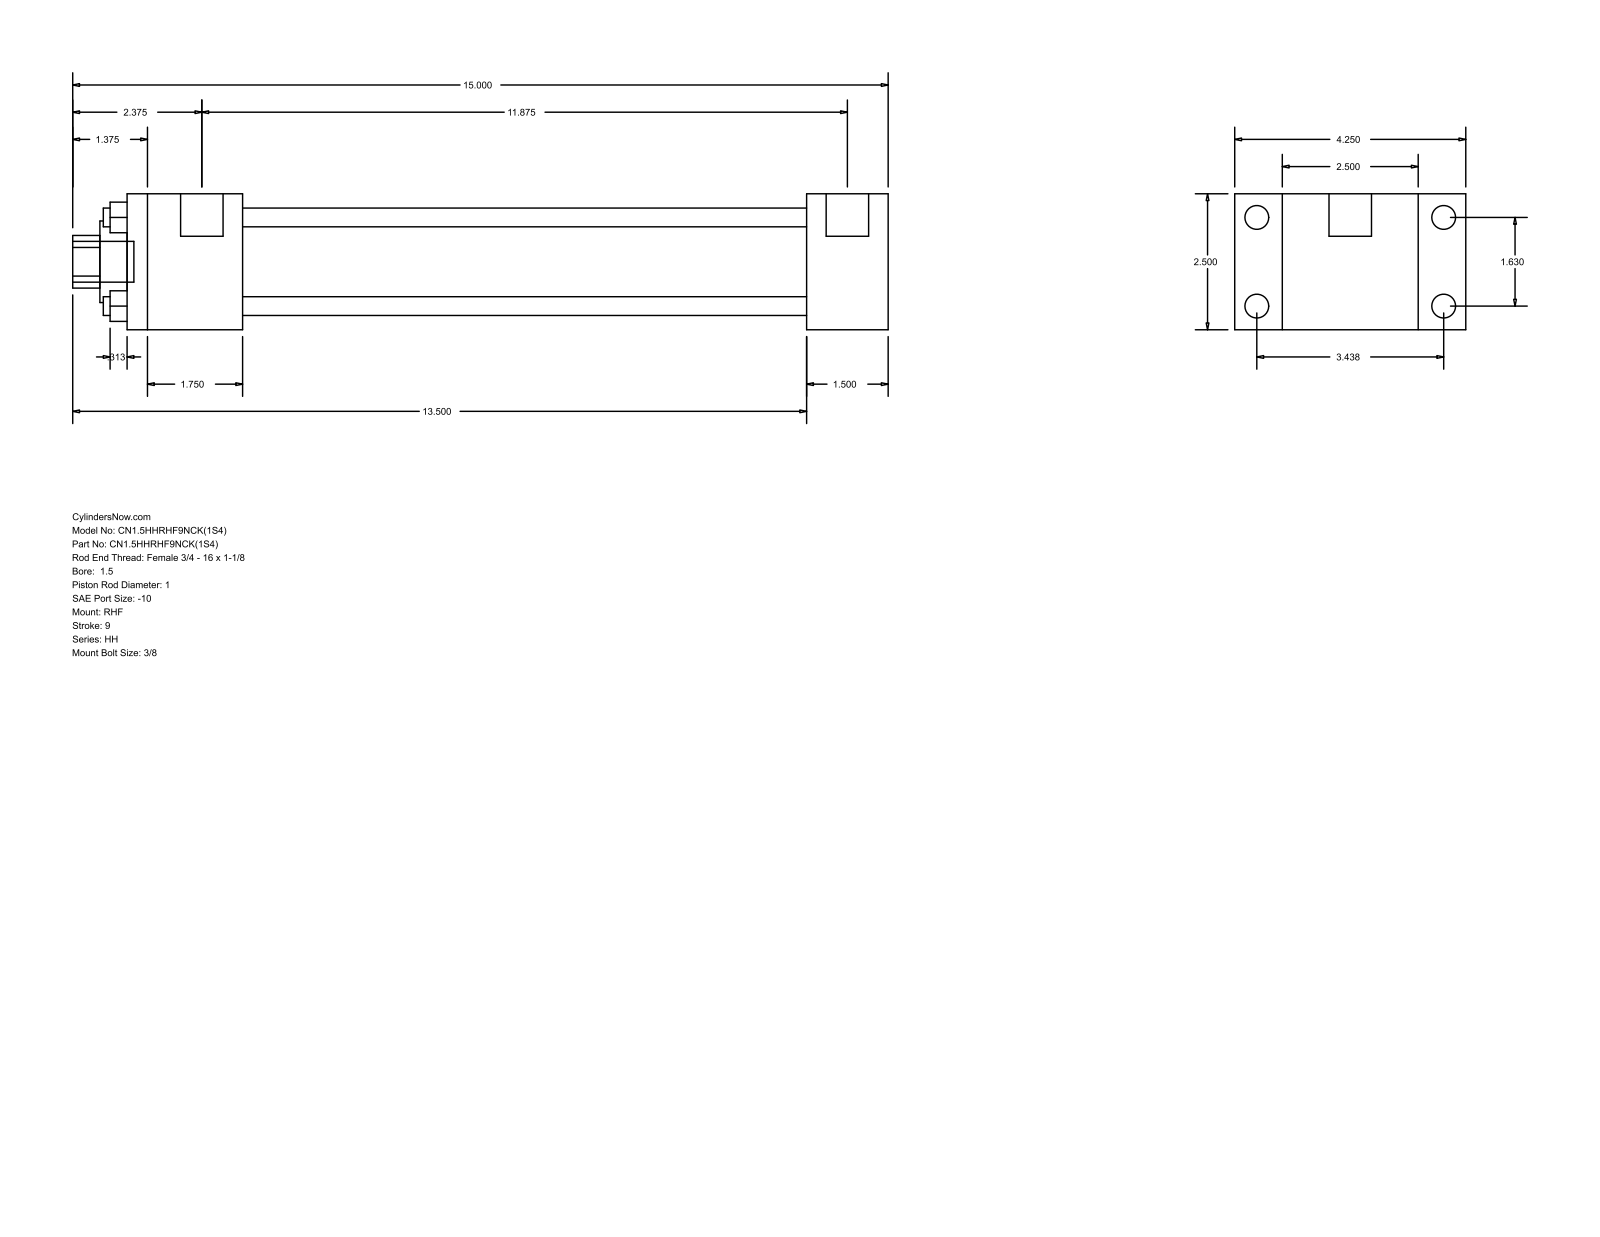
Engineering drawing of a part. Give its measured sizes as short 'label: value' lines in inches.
name: HH_RHF__0150_1
written by: GSSL Pune (CONFIG_CONTROL_DESIGN)
unit: in
bodies: 0 solids, 88 faces (60 planar, 28 cylindrical, 0 other)
size: 15 × 4.25 × 2.5
holes: 4× ⌀0.345, 1× ⌀1, 1× ⌀1.5, 1× ⌀1.75
bosses: 4× ⌀0.438, 4× ⌀0.219, 2× ⌀0.781, 1× ⌀0.75
rounds: 1× R0.484
face distances: 2.5, 0.875, 3.375, 1.5, 4.25, 10.375, 11.875, 2.125, 12.5, 14
hole spacings: 1.152, 1.63, 2.305
